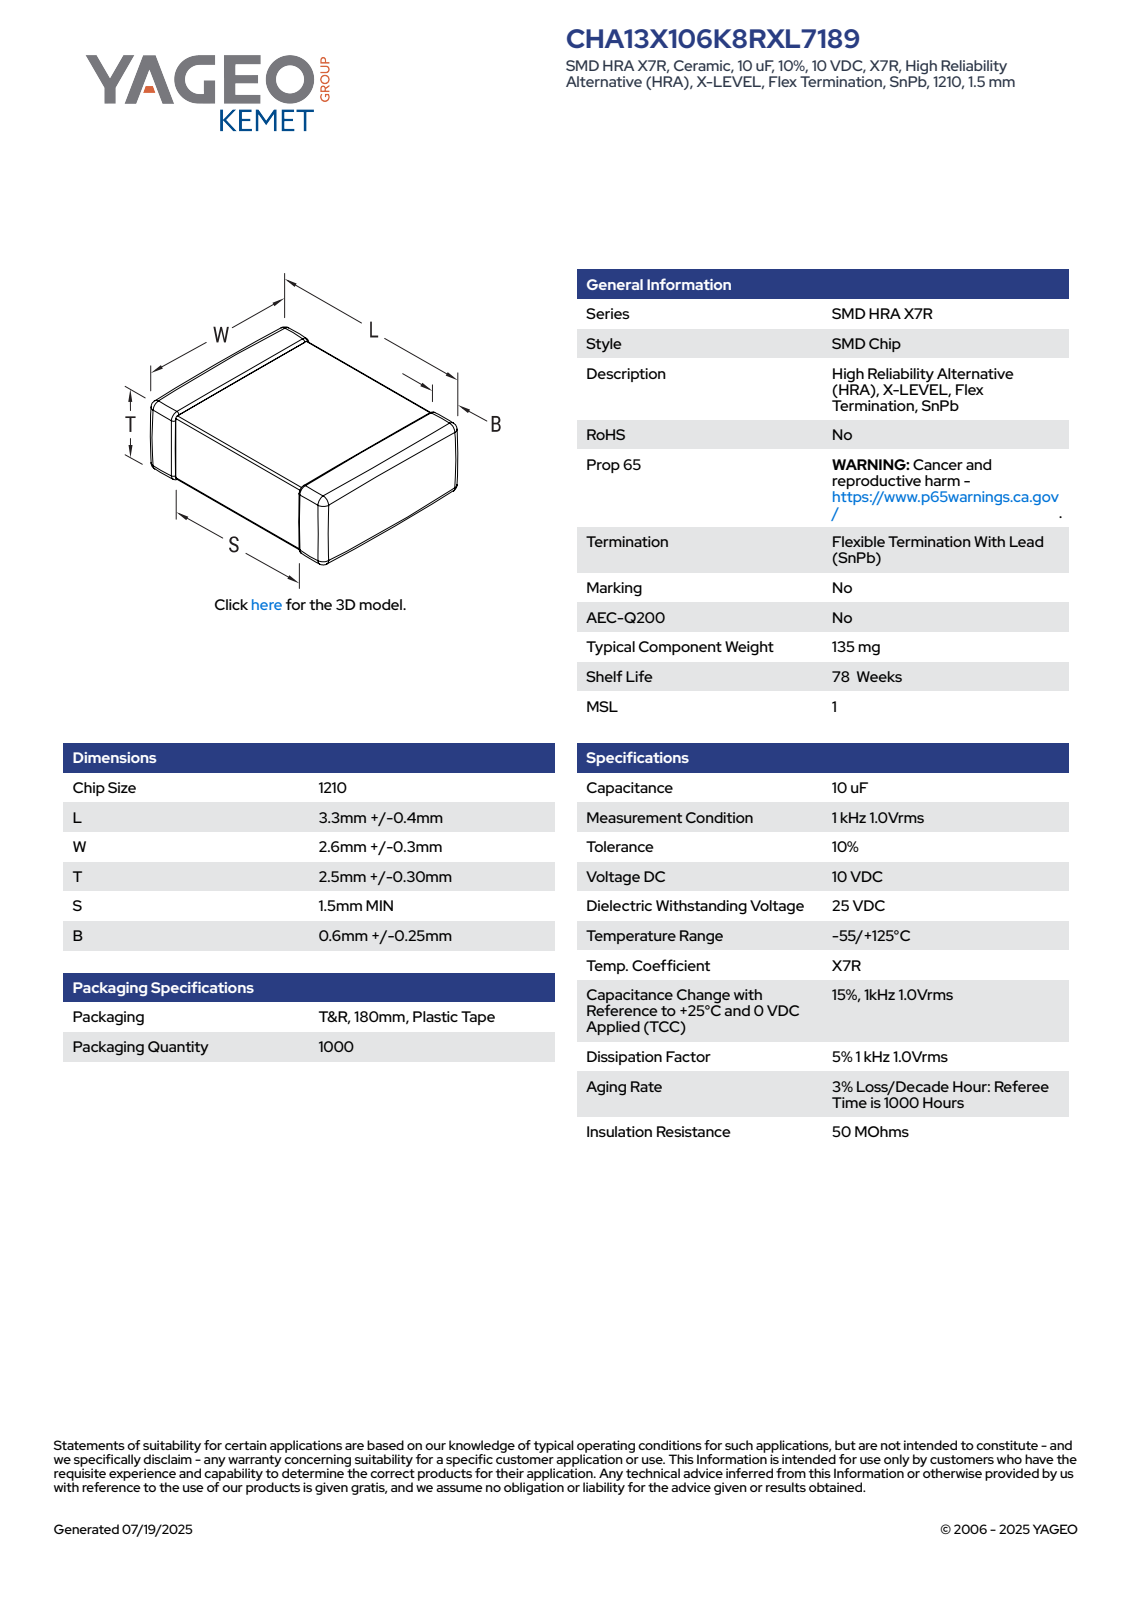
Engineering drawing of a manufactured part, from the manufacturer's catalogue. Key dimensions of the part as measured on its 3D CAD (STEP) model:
Part name (STEP PRODUCT): CCSM_STD_1210_L3.7W2.9T2.8S2.5B0.85
STEP written by: SolidWorks 2021 (AUTOMOTIVE_DESIGN)
Units: millimetres
Bodies: 4 solids, 125 faces (71 planar, 38 cylindrical, 16 other)
Overall size (bounding box): 3.7 × 2.9 × 2.8
Volume: 29 mm³ · Surface area: 58 mm²
Main face-to-face distances: 2.74, 2.84, 3.7, 2.68, 2.78, 2.8, 2.9, 0.43, 1.57, 2.13
